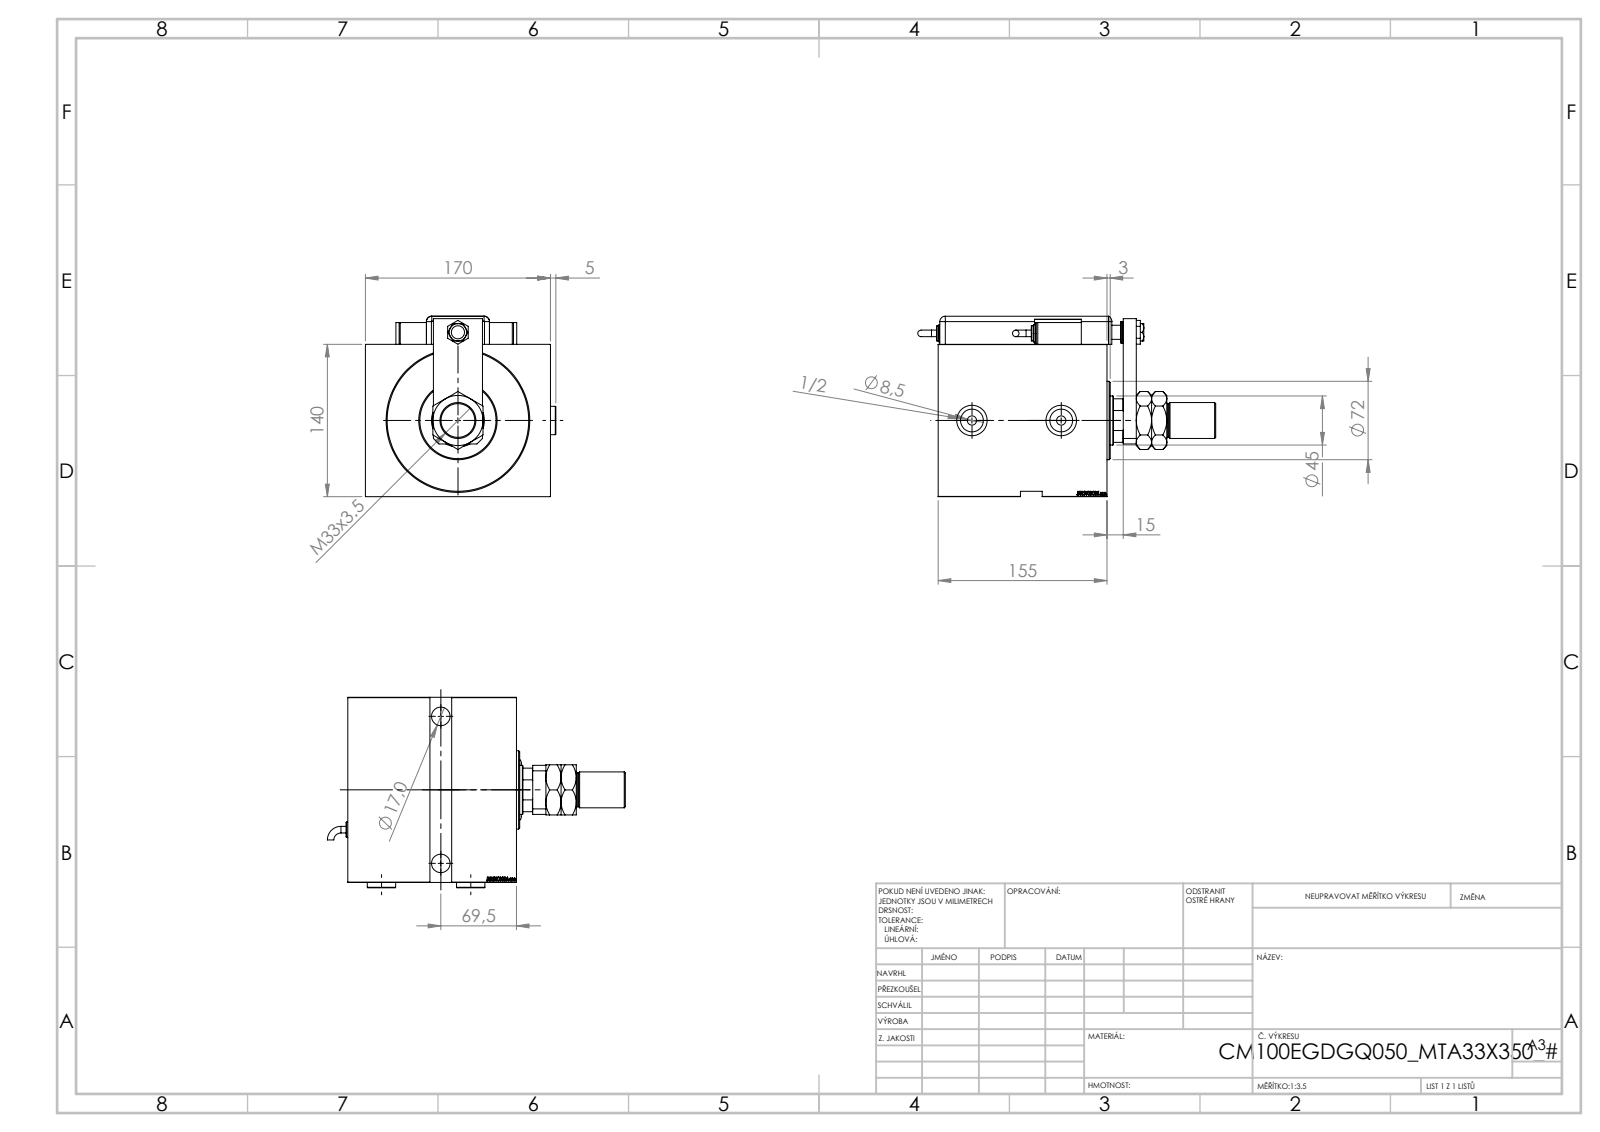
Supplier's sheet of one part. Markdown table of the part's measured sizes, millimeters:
| quantity | value |
| --- | --- |
| part name | Q_T_W_MTA; SWITCH_Q_FRONT_BACK; MAGNETIC SWITCH Q; NUT_D13 (+7 more) |
| STEP written by | SolidWorks 2019 (CONFIG_CONTROL_DESIGN) |
| units | millimeters |
| bodies | 16 solids, 1335 faces (665 planar, 119 cylindrical, 551 other) |
| overall size | 273.76 × 174.9 × 165.8 |
| volume | 3 566 000 mm³ |
| surface area | 380 893 mm² |
| round holes (diameter × count) | 4 × 2, 8 × 2, 8.5 × 2, 17 × 2, 20.96 × 2, 25 × 2, 28 × 2, 12 × 1, 13 × 1, 14 × 1, 31.5 × 1, 33 × 1 |
| round bosses / shafts (diameter × count) | 20 × 3, 26 × 2, 16 × 2, 14 × 2, 6 × 2, 102 × 1, 72 × 1, 31 × 1 |
| partial cylindrical surfaces (radius × count) | 5 × 9, 10 × 1, 22 × 1 |
| main face-to-face distances | 170, 155, 140, 3, 129, 26, 5, 150, 124, 20 |
| hole center spacings | 85.67, 100.19, 20, 81, 82, 135 |
